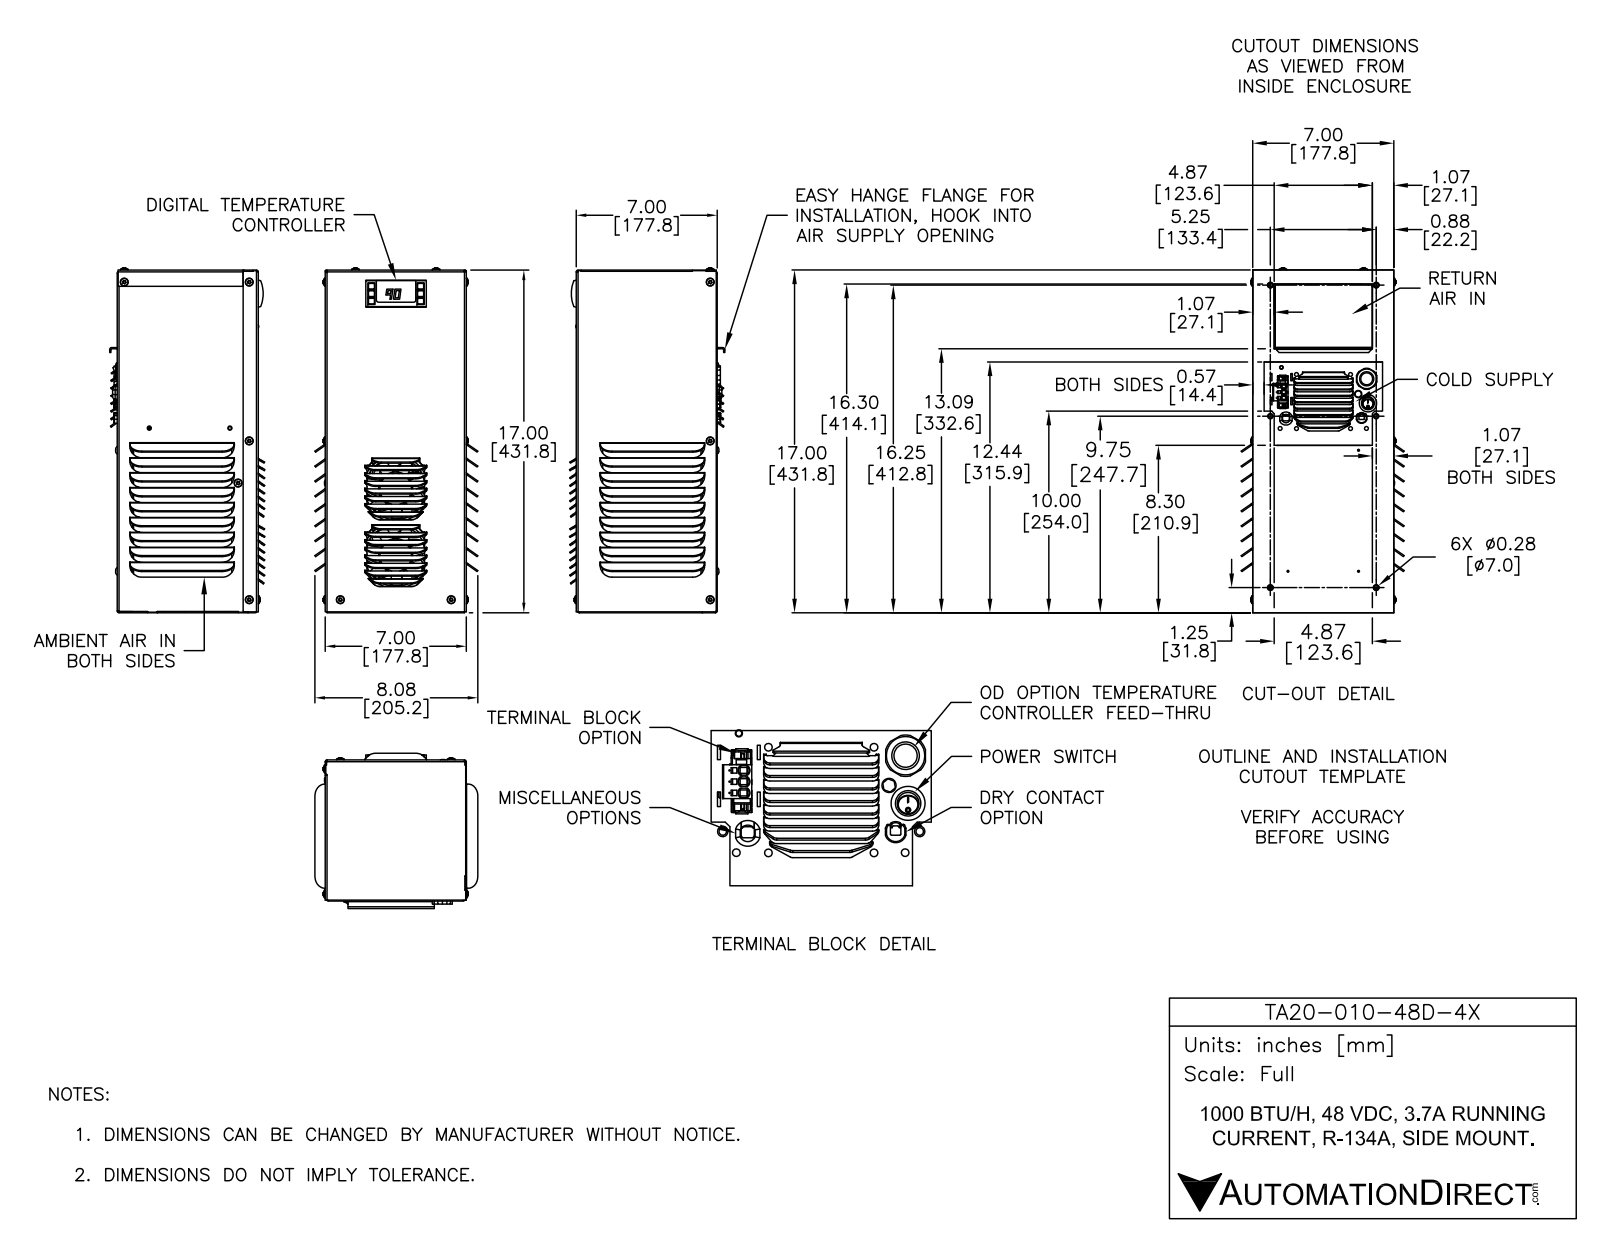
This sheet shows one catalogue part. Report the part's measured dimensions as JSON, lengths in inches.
{"part_name": "TA20-010-48D-4X", "step_written_by": "SolidWorks 2019 (AUTOMOTIVE_DESIGN)", "units": "inches", "bodies": {"solids": 70, "faces": 3570, "planar": 1682, "cylindrical": 1401, "other": 487}, "overall_size": [17.092, 8.079, 7.704], "volume_in3": 93.28, "surface_area_in2": 1758, "round_holes": [[0.203, 16], [0.325, 16], [0.33, 16], [0.28, 14], [0.219, 10], [0.193, 8], [0.2, 6], [0.201, 6], [0.272, 6], [0.109, 5], [0.195, 4], [0.156, 2]], "round_bosses_or_shafts": [[0.19, 17], [0.329, 14], [0.313, 10], [0.564, 6], [0.44, 6], [0.344, 6], [0.326, 6], [0.321, 6]], "partial_cylinders_radius": [[0.01, 100], [0.125, 91], [0.005, 90], [0.031, 81], [0.015, 77], [0.091, 57], [0.03, 53], [0.594, 36]], "face_to_face_distances": [0.06, 6.938, 0.06, 6.998, 6.935, 6.875, 6.875, 6.815, 6.878, 16.938], "hole_center_spacings": [0.8, 1, 1.601, 1.625, 1.25, 2, 2.359, 1.94]}
